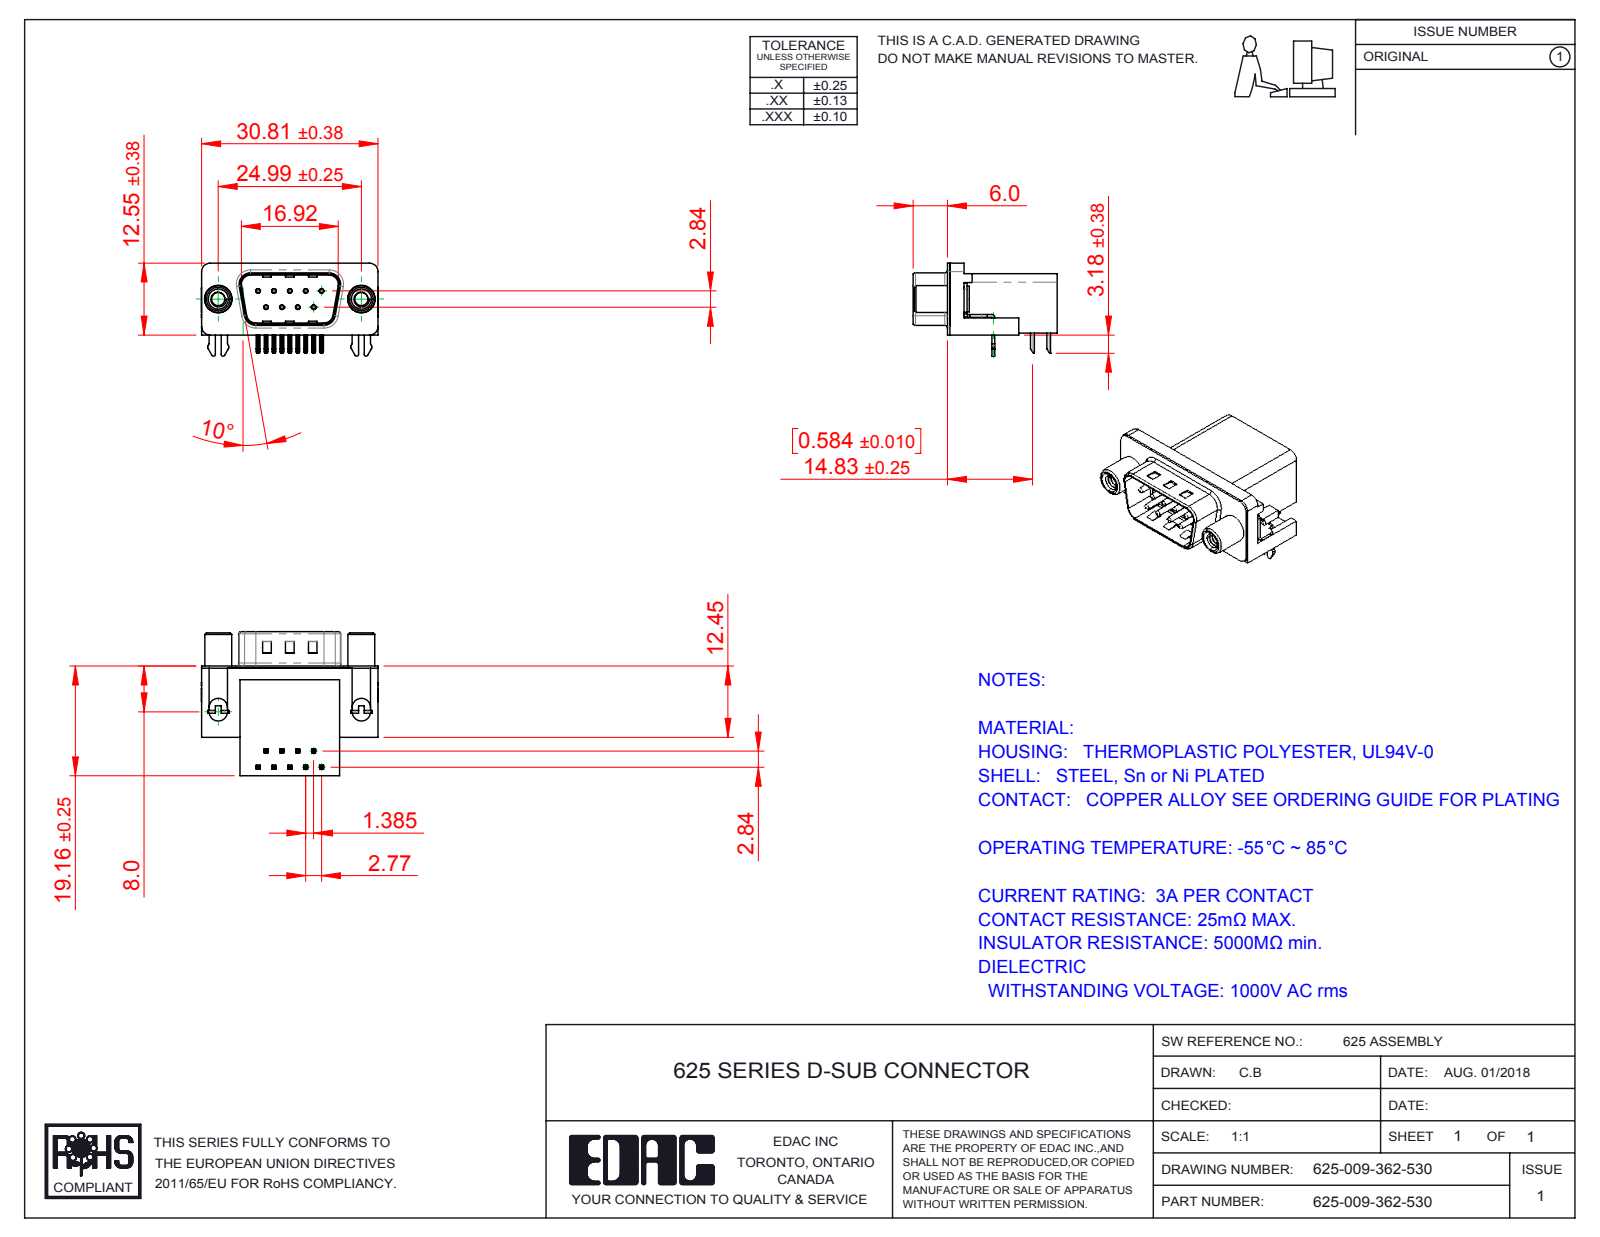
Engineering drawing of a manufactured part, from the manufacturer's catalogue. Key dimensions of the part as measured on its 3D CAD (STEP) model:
Part name (STEP PRODUCT): 625 2 Prong Board Lock; 625-009-362-530; 625 Contact Top; 625 Shell_9 Socket (+3 more)
STEP written by: SolidWorks 2016 (CONFIG_CONTROL_DESIGN)
Units: millimetres
Bodies: 15 solids, 1027 faces (597 planar, 333 cylindrical, 97 other)
Overall size (bounding box): 30.89 × 25.16 × 16.25
Volume: 4 565 mm³ · Surface area: 5 156 mm²
Round holes (diameter × count): ⌀0.35 ×9, ⌀0.8 ×9, ⌀2.3 ×2, ⌀3.1 ×2, ⌀4 ×2, ⌀4.8 ×2, ⌀5 ×2
Round bosses / shafts (diameter × count): ⌀0.75 ×9, ⌀4.9 ×2, ⌀4.7 ×2, ⌀4.5 ×2, ⌀3.85 ×2
Partial cylindrical surfaces — rounded edges, fillets, slot ends (radius × count): R0.25 ×36, R0.12 ×18, R1 ×16, R0.5 ×14, R1.5 ×8, R1.6 ×8, R0.32 ×4, R0.9 ×4
Main face-to-face distances: 0.4, 10.34, 18.76, 19.16, 16.26, 2.5, 2.9, 0.35, 10.69, 6.7
Hole centre spacings: 3.16, 2.77, 5.54, 5.03, 5.04, 8.31, 7.48, 7.49
